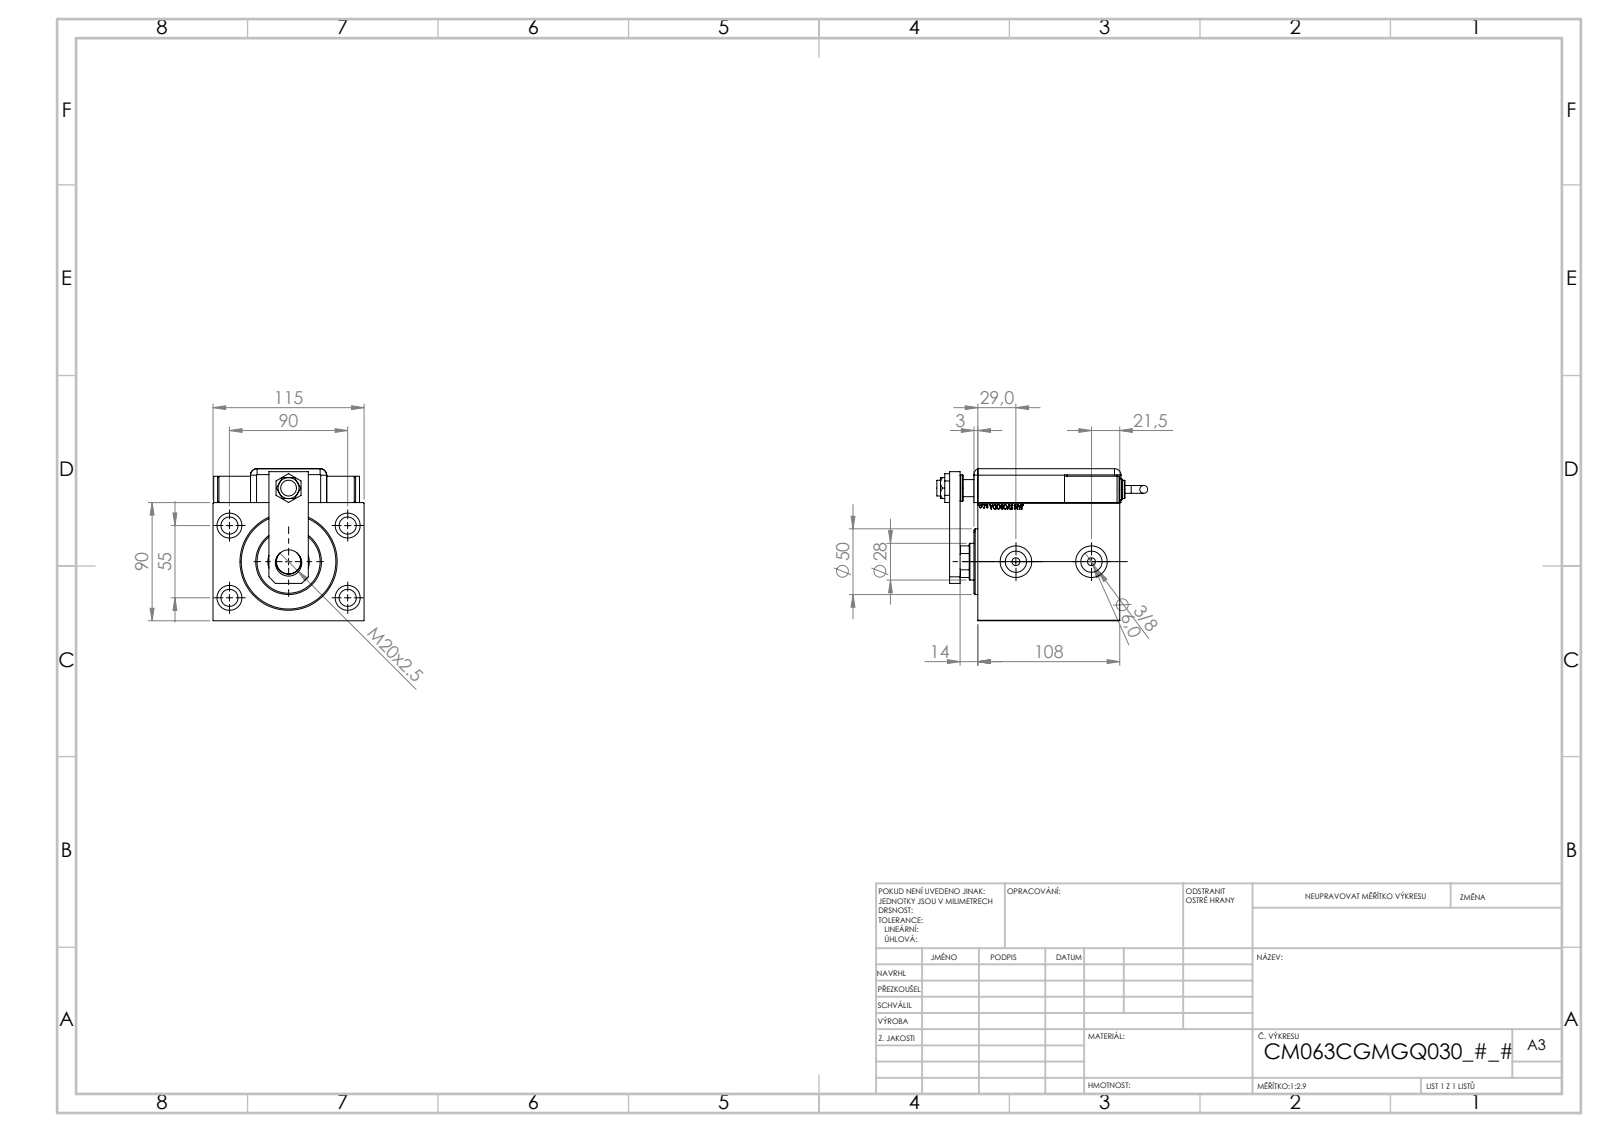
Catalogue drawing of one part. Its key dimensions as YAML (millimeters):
part_name: "SWITCH_Q_FRONT_BACK; NUT_D13; V450CM_C_Body; V450CM_C_VCP (+7 more)"
step_written_by: "SolidWorks 2019 (CONFIG_CONTROL_DESIGN)"
units: millimeters
bodies: {solids: 13, faces: 1250, planar: 616, cylindrical: 117, other: 517}
overall_size: [160.46, 115.8, 115]
volume: 1116000
surface_area: 196592
round_holes:
  - {diameter: 13, count: 5}
  - {diameter: 19, count: 4}
  - {diameter: 4, count: 2}
  - {diameter: 6, count: 2}
  - {diameter: 8, count: 2}
  - {diameter: 16.17, count: 2}
  - {diameter: 24, count: 2}
  - {diameter: 12, count: 1}
  - {diameter: 14, count: 1}
  - {diameter: 18.5, count: 1}
  - {diameter: 20, count: 1}
  - {diameter: 28, count: 1}
round_bosses_or_shafts:
  - {diameter: 20, count: 3}
  - {diameter: 16, count: 2}
  - {diameter: 14, count: 2}
  - {diameter: 6, count: 2}
  - {diameter: 50, count: 1}
partial_cylinders:
  - {radius: 5, count: 9}
  - {radius: 10, count: 1}
  - {radius: 13.5, count: 1}
face_to_face_distances: [90, 3, 108, 115, 19, 89, 8, 25.8, 115.8, 20]
hole_center_spacings: [52.74, 53.27, 52.22, 55, 90, 94.85, 105.48, 1]
